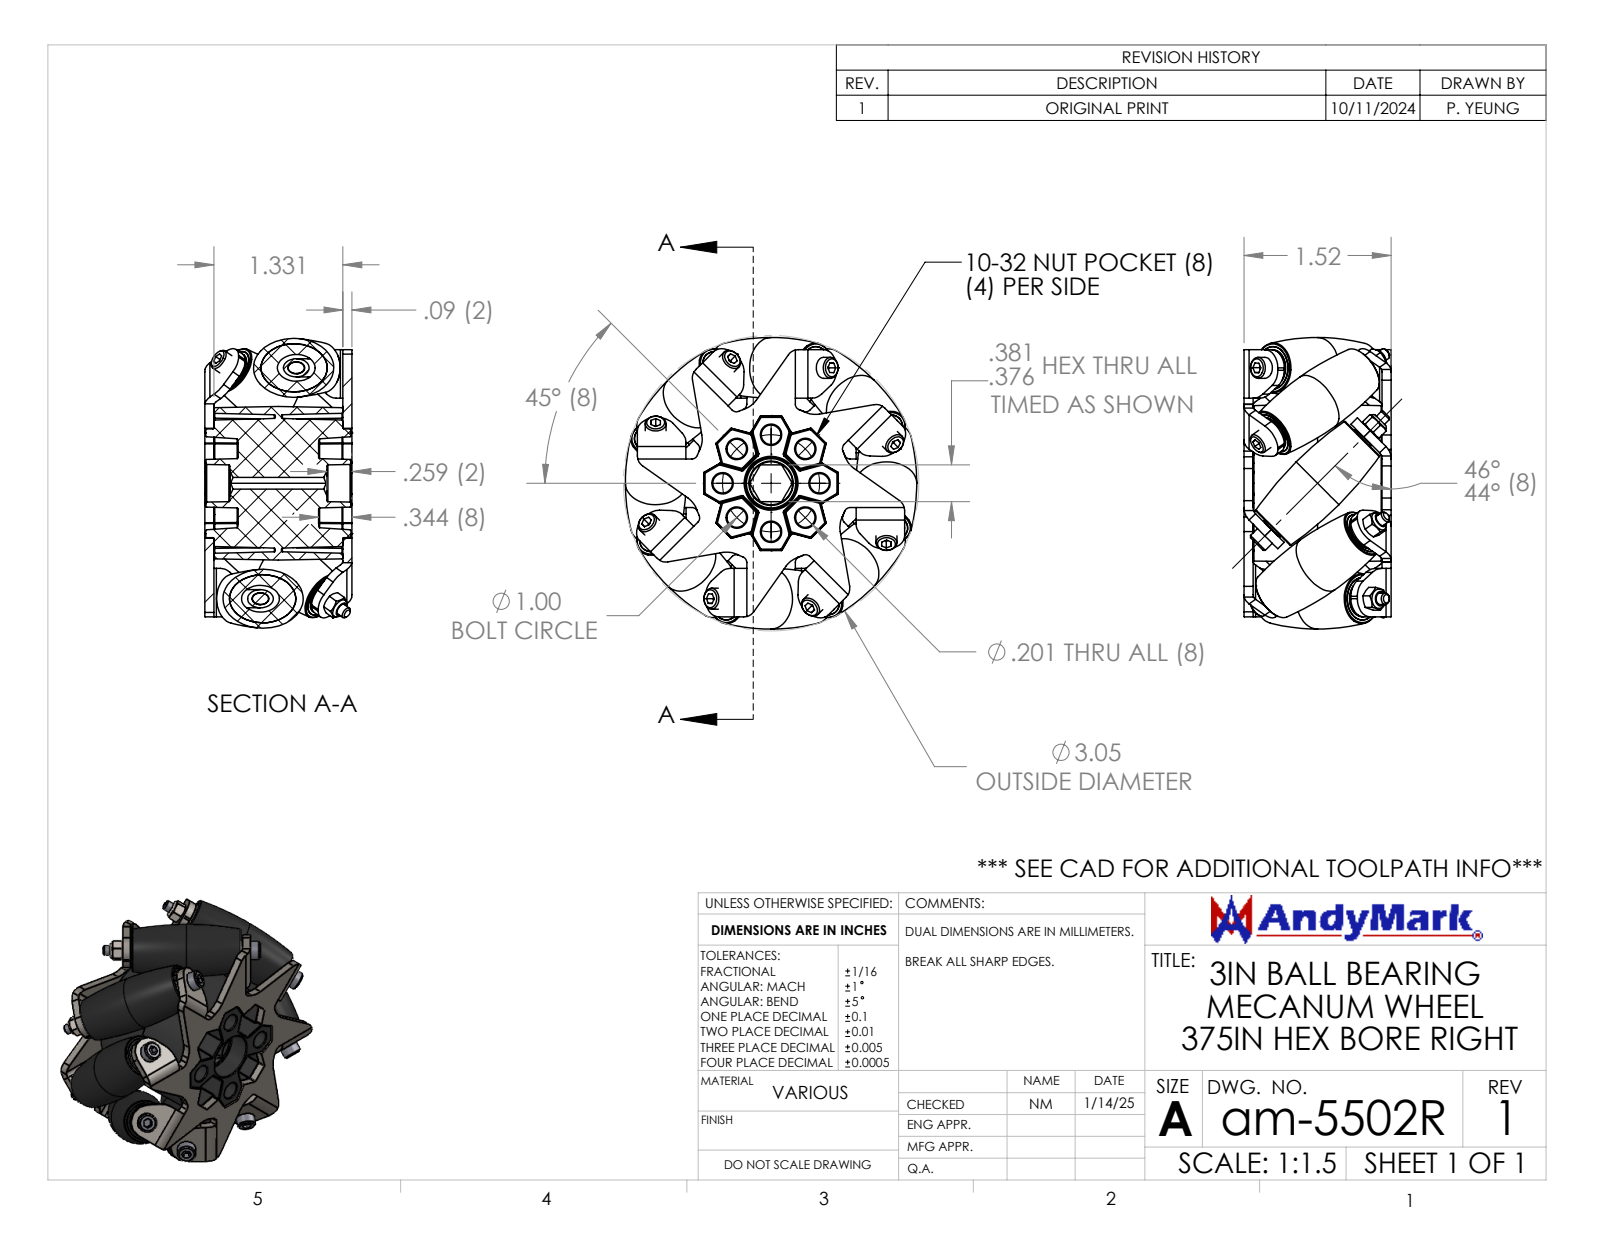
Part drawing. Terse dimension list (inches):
name: am-4764 4IN BB Mecanum Axle Sleeve; am-5501R_plate 3IN BB Mecanum Right Plate; am-5502_hub 3IN Ball Bearing Mecanum Hub, 375IN Hex Bore; am-3681 3-16 in ID 3-8 in OD Shielded Bearing Extended Inner Race_57155K384 (+6 more)
written by: SolidWorks 2024 (AUTOMOTIVE_DESIGN)
unit: in
bodies: 299 solids, 2973 faces (640 planar, 1026 cylindrical, 1307 other)
size: 3.005 × 3.005 × 1.519
volume: 5.176 in³; area: 142.6 in²
holes: 15× ⌀0.134, 14× ⌀0.187, 14× ⌀0.234, 14× ⌀0.303, 14× ⌀0.438, 8× ⌀0.123, 8× ⌀0.125, 8× ⌀0.201, 8× ⌀0.276, 8× ⌀0.375
bosses: 14× ⌀0.375, 8× ⌀0.217, 8× ⌀0.118
rounds: 270× R0.01, 32× R0.25, 19× R0.188, 16× R0.09, 16× R0.125, 16× R0.184, 10× R0.062, 7× R0.187
face distances: 0.094, 1.425, 1.441, 1.179, 1.331, 1.519, 0.115, 1.347, 0.022, 1.326
hole spacings: 0.383, 0.707, 0.924, 1
